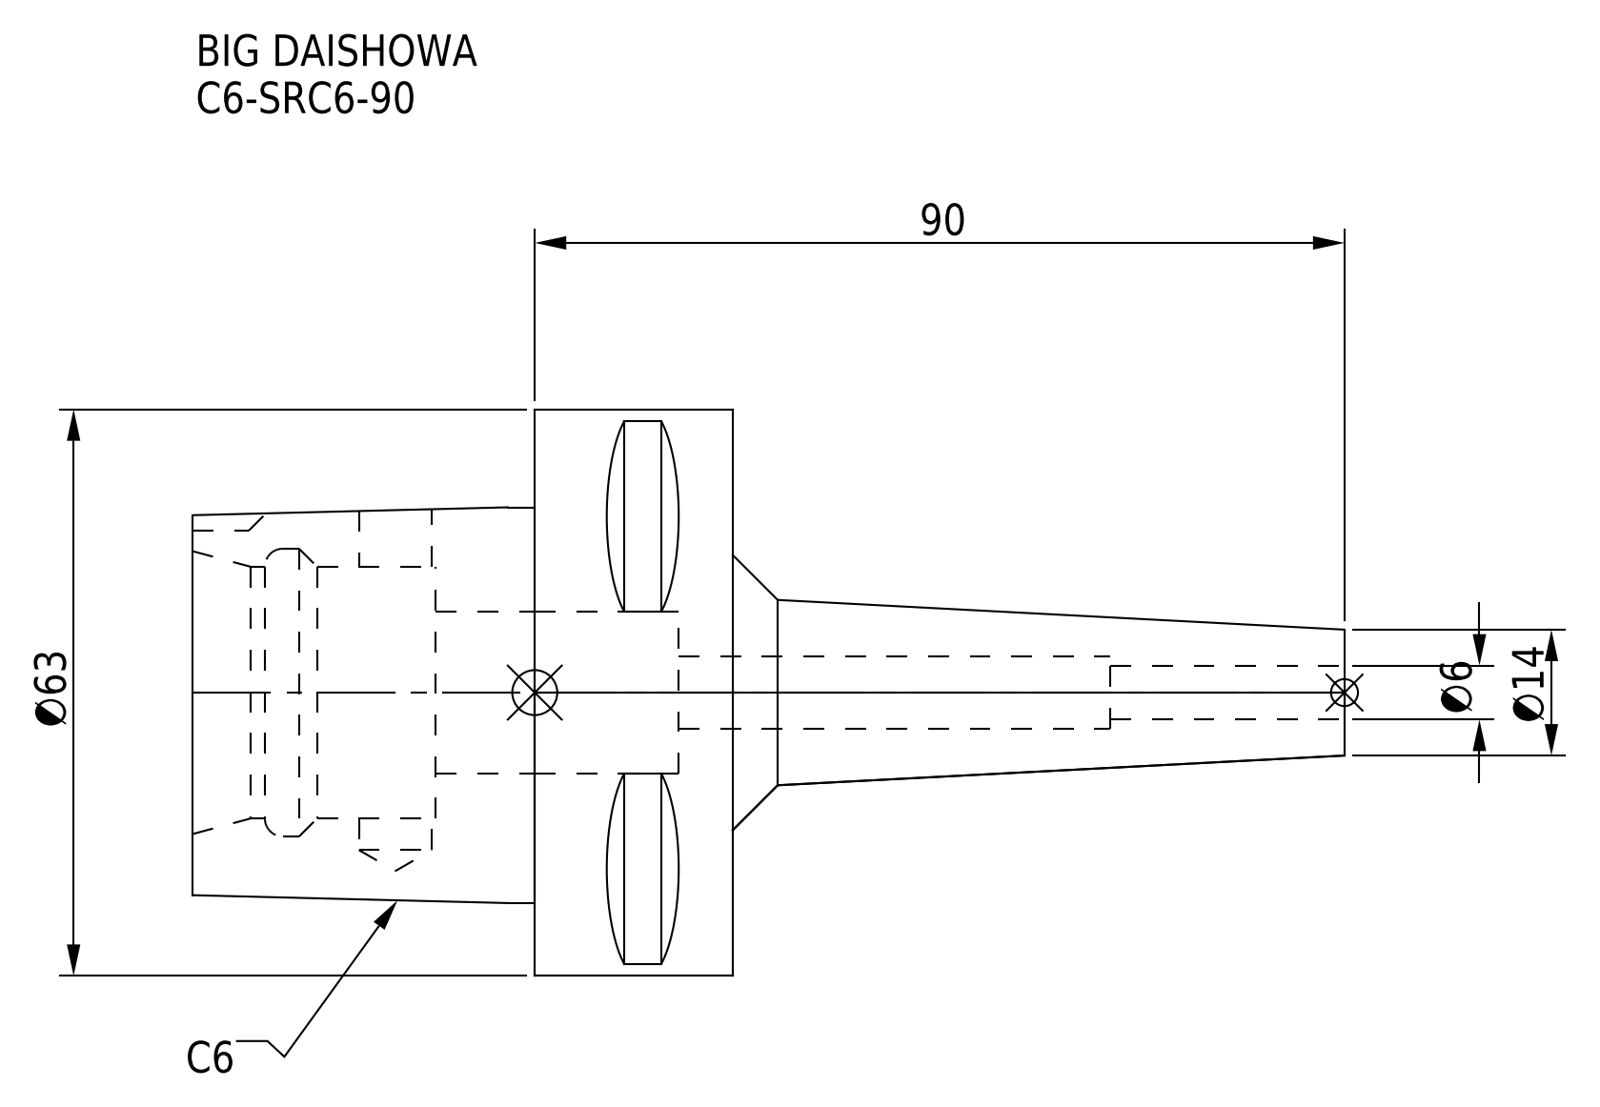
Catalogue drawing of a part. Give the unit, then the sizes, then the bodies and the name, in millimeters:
Units: millimetres
Overall size (bounding box): 128 × 63 × 63
Round holes (diameter × count): ⌀6 ×1, ⌀8 ×1, ⌀8.1 ×1, ⌀18 ×1, ⌀28 ×1, ⌀32 ×1
Round bosses / shafts (diameter × count): ⌀63 ×1
Partial cylindrical surfaces — rounded edges, fillets, slot ends (radius × count): R5 ×1
Main face-to-face distances: 22, 27, 60, 38, 33, 11, 24.89, 55.4, 6, 16
Volume: 111 036 mm³ · Surface area: 25 206 mm²
Bodies: 1 solid, 62 faces (29 planar, 19 cylindrical, 14 other)
Part name (STEP PRODUCT): C6-SRC6-90
STEP written by: CREO PARAMETRIC BY PTC INC, 2016380 (AUTOMOTIVE_DESIGN)
